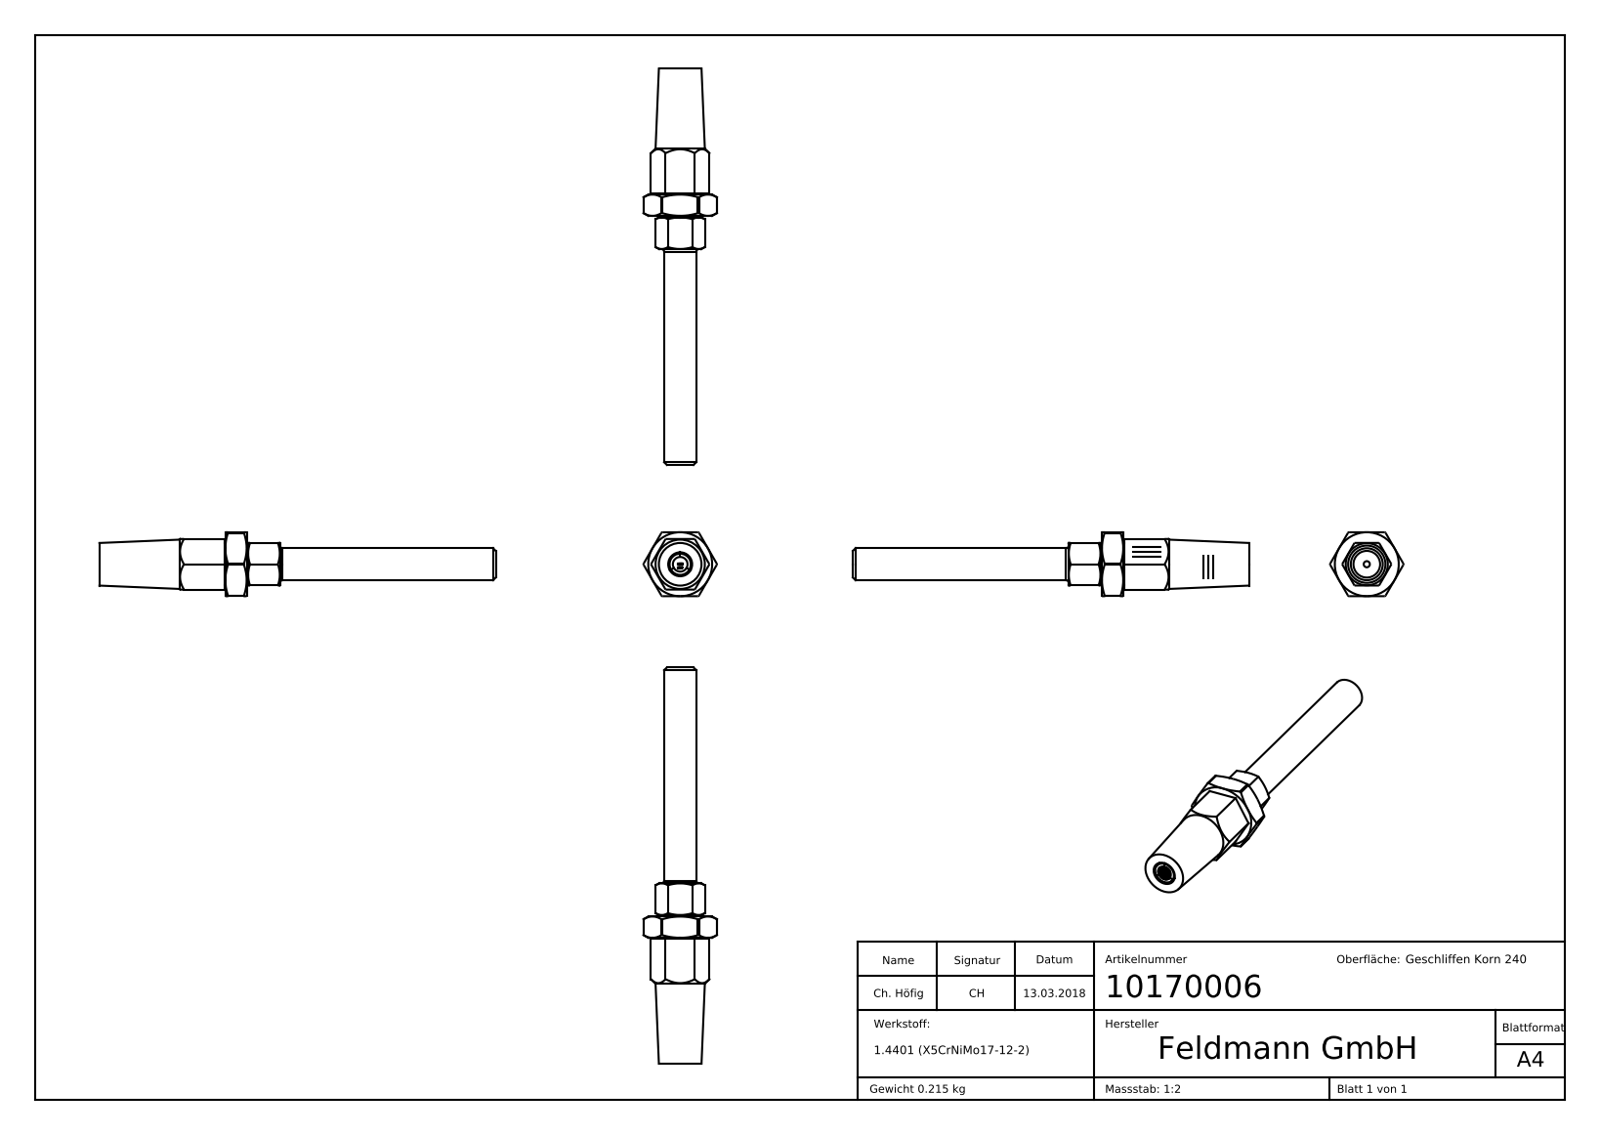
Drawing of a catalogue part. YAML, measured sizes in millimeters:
part_name: "1017000X Teil4_10170006 Teil4; 1017000X Teil2_10170006 Teil2; 10170006; 1017000X Teil5_10170006 Teil5 (+3 more)"
step_written_by: "SolidWorks 2015 (CONFIG_CONTROL_DESIGN)"
units: millimeters
bodies: {solids: 8, faces: 576, planar: 140, cylindrical: 153, other: 283}
overall_size: [148.75, 27.56, 24]
volume: 26806
surface_area: 13889
round_holes:
  - {diameter: 14, count: 2}
  - {diameter: 2.3, count: 1}
  - {diameter: 5.5, count: 1}
  - {diameter: 7, count: 1}
  - {diameter: 7.5, count: 1}
  - {diameter: 9.97, count: 1}
round_bosses_or_shafts:
  - {diameter: 16, count: 1}
  - {diameter: 12, count: 1}
partial_cylinders:
  - {radius: 0.5, count: 6}
face_to_face_distances: [4, 20, 19, 16, 24, 8, 17.49, 1.51, 1.49, 17.51]
